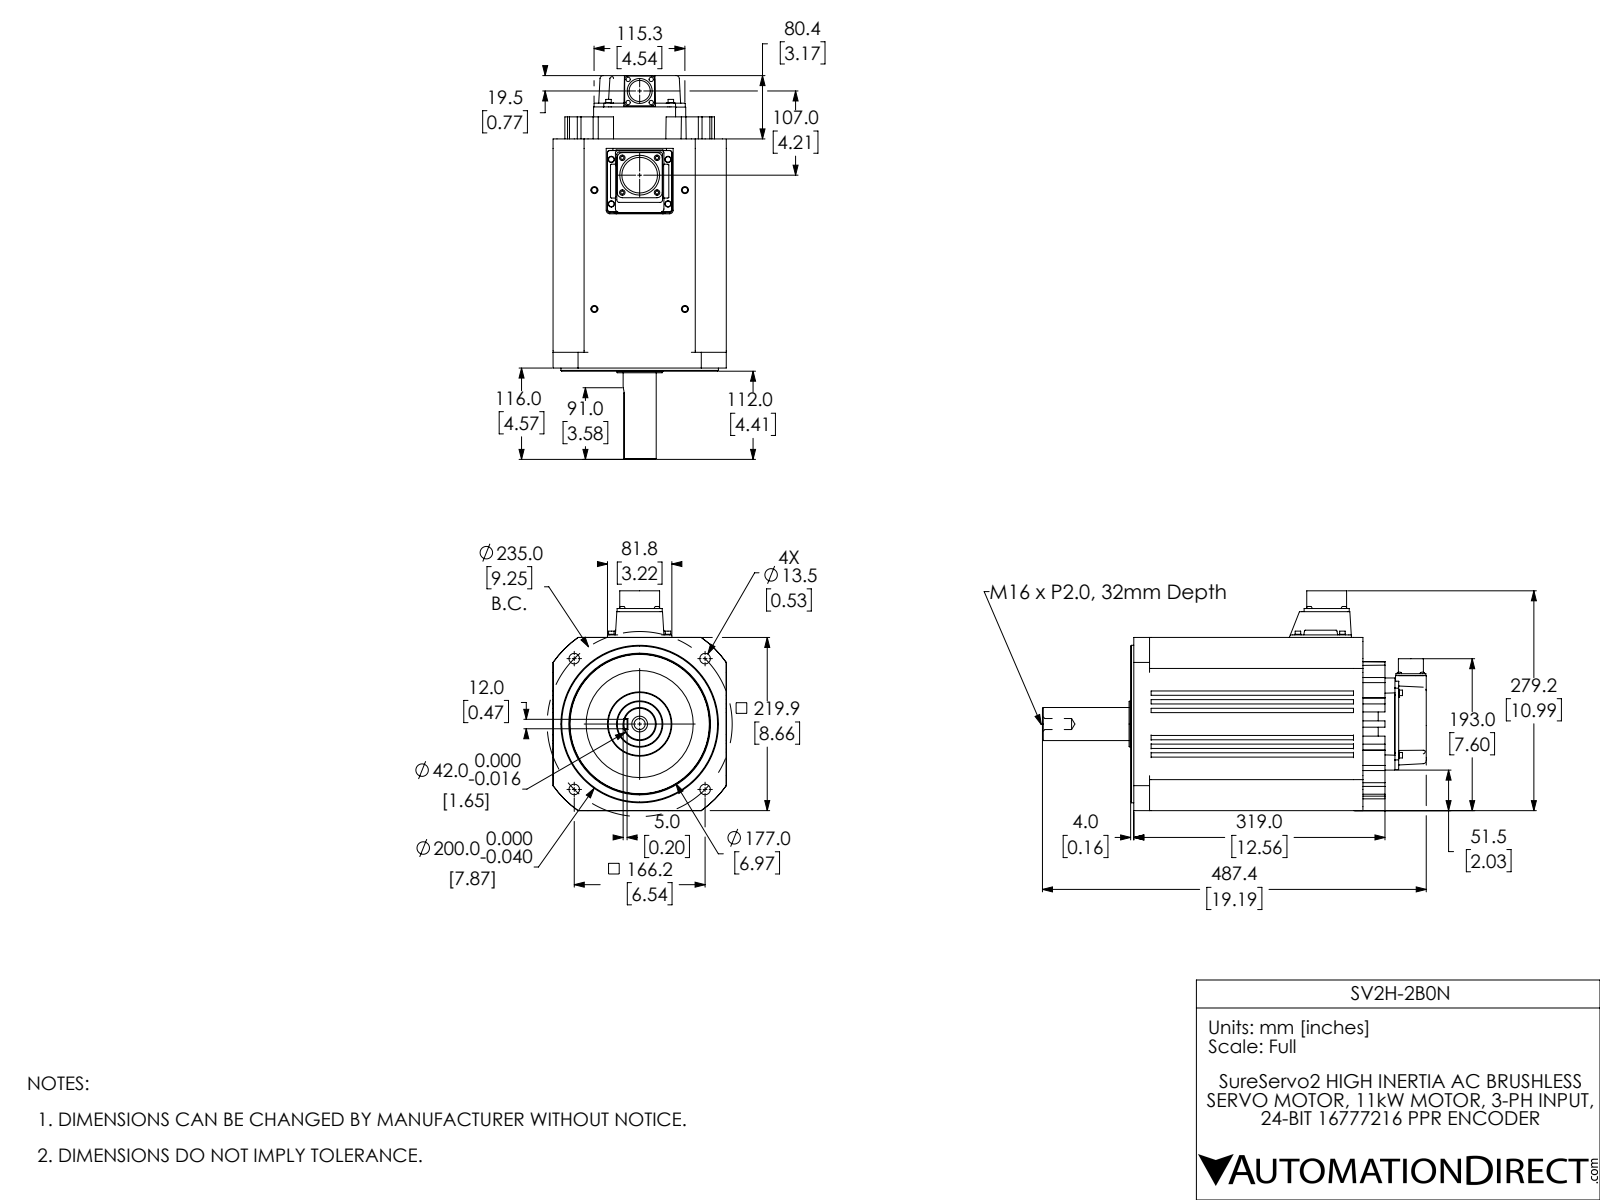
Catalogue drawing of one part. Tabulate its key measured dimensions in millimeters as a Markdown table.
| quantity | value |
| --- | --- |
| part name | SV2H-2B0N Ext |
| STEP written by | SolidWorks 2017 (AUTOMOTIVE_DESIGN) |
| units | millimeters |
| bodies | 1 solid, 803 faces (361 planar, 233 cylindrical, 209 other) |
| overall size | 487.5 × 279.2 × 220 |
| volume | 13 570 000 mm³ |
| surface area | 516 000 mm² |
| round holes (diameter × count) | 4.3 × 4, 4.6 × 4, 6.8 × 4, 13.5 × 4, 14 × 1, 26.9 × 1, 45.3 × 1, 180 × 1 |
| round bosses / shafts (diameter × count) | 8 × 8, 7 × 8, 4 × 4, 200 × 1, 178 × 1, 136 × 1, 58.8 × 1, 50.6 × 1 |
| partial cylindrical surfaces (radius × count) | 0.8 × 24, 0.5 × 23, 5 × 18, 3 × 14, 4 × 8, 6 × 5, 1 × 4, 6.6 × 4 |
| main face-to-face distances | 220, 39.4, 180.6, 5.5, 11, 141.2, 4, 62, 67.5, 16.5 |
| hole center spacings | 117.5, 166.2, 27.8, 41.2, 44.5, 51.3, 56.5, 60.5 |
